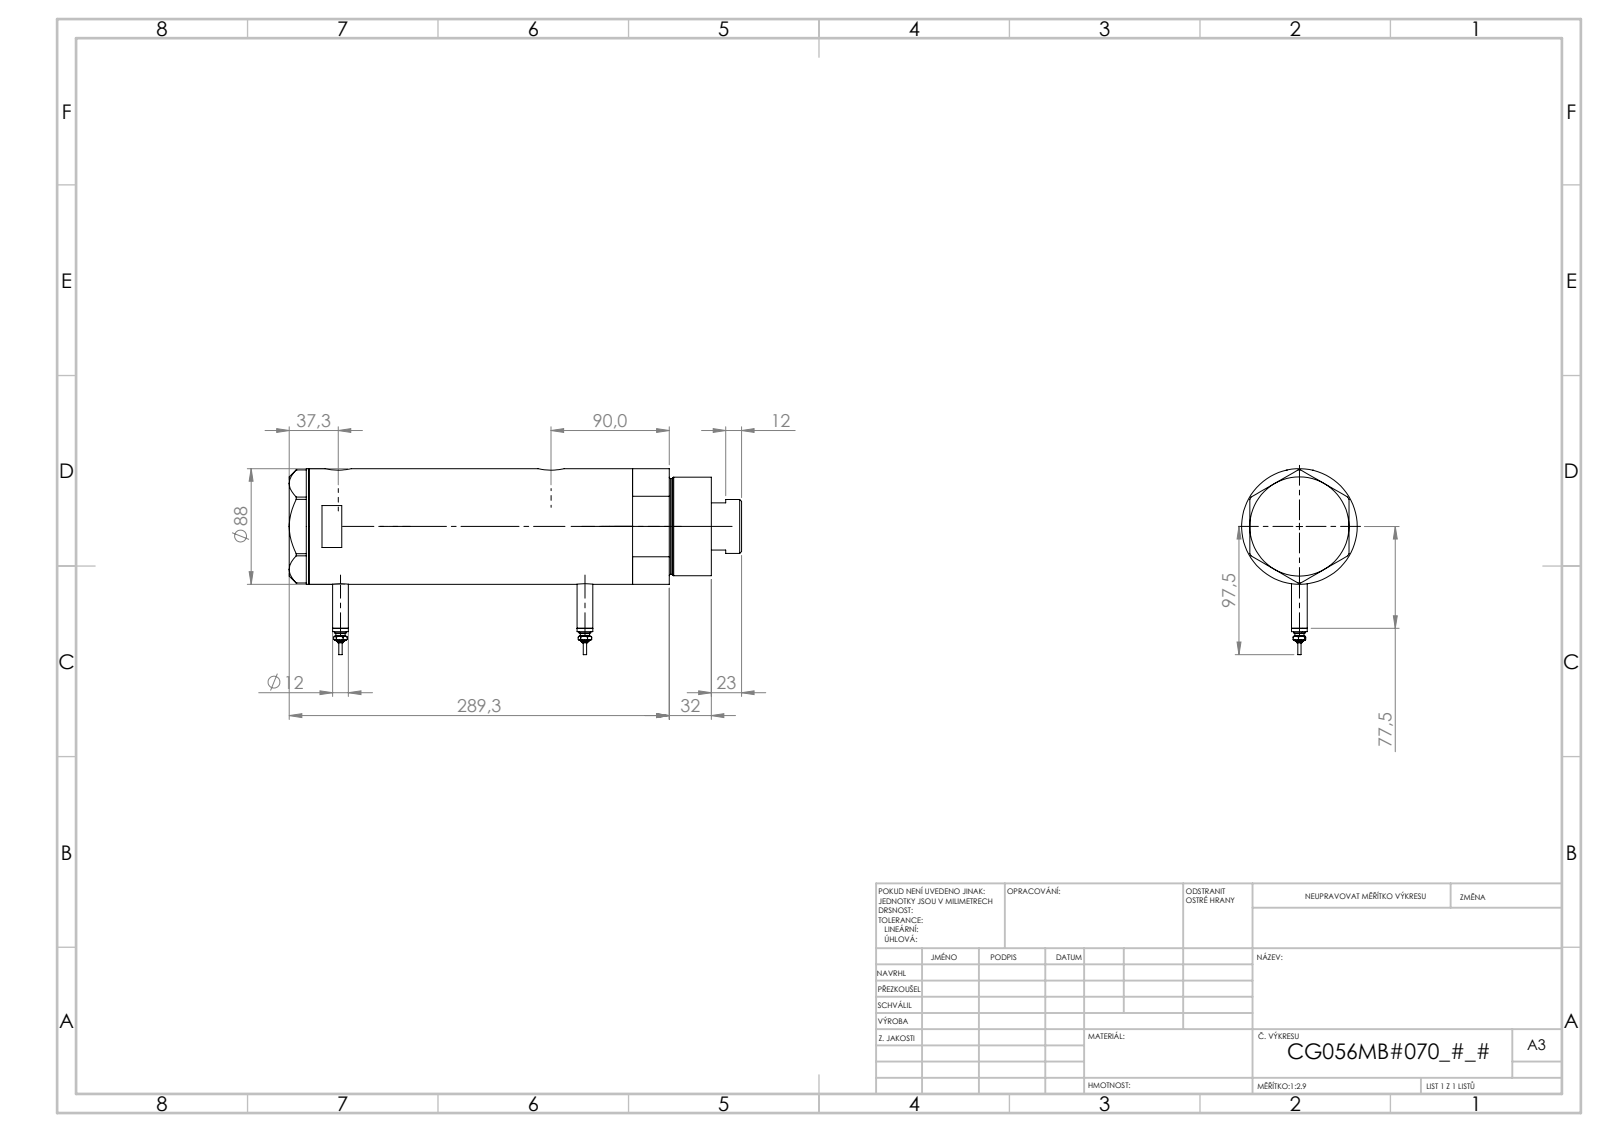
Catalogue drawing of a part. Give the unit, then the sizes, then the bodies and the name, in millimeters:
Units: millimetres
Overall size (bounding box): 344.3 × 141.5 × 88
Round holes (diameter × count): ⌀12.5 ×2, ⌀13.16 ×2, ⌀20 ×2, ⌀14.5 ×1, ⌀42 ×1, ⌀43.5 ×1, ⌀56 ×1, ⌀60 ×1, ⌀80 ×1
Round bosses / shafts (diameter × count): ⌀12 ×2, ⌀9 ×2, ⌀7 ×2, ⌀4.5 ×2, ⌀2.5 ×2, ⌀88 ×1, ⌀75 ×1, ⌀73 ×1
Main face-to-face distances: 184.4, 26, 158.4, 15, 41, 199.4, 306.3, 321.3, 280.3, 121.9
Hole centre spacings: 1.7, 25.8, 160.3, 162, 186.1, 187.8
Volume: 1 824 000 mm³ · Surface area: 255 126 mm²
Bodies: 6 solids, 213 faces (80 planar, 69 cylindrical, 64 other)
Part name (STEP PRODUCT): V270CG_BACK; V270CG_MIDDLE; V270CG_VC; V270CG_FRONT (+1 more)
STEP written by: SolidWorks 2019 (CONFIG_CONTROL_DESIGN)
